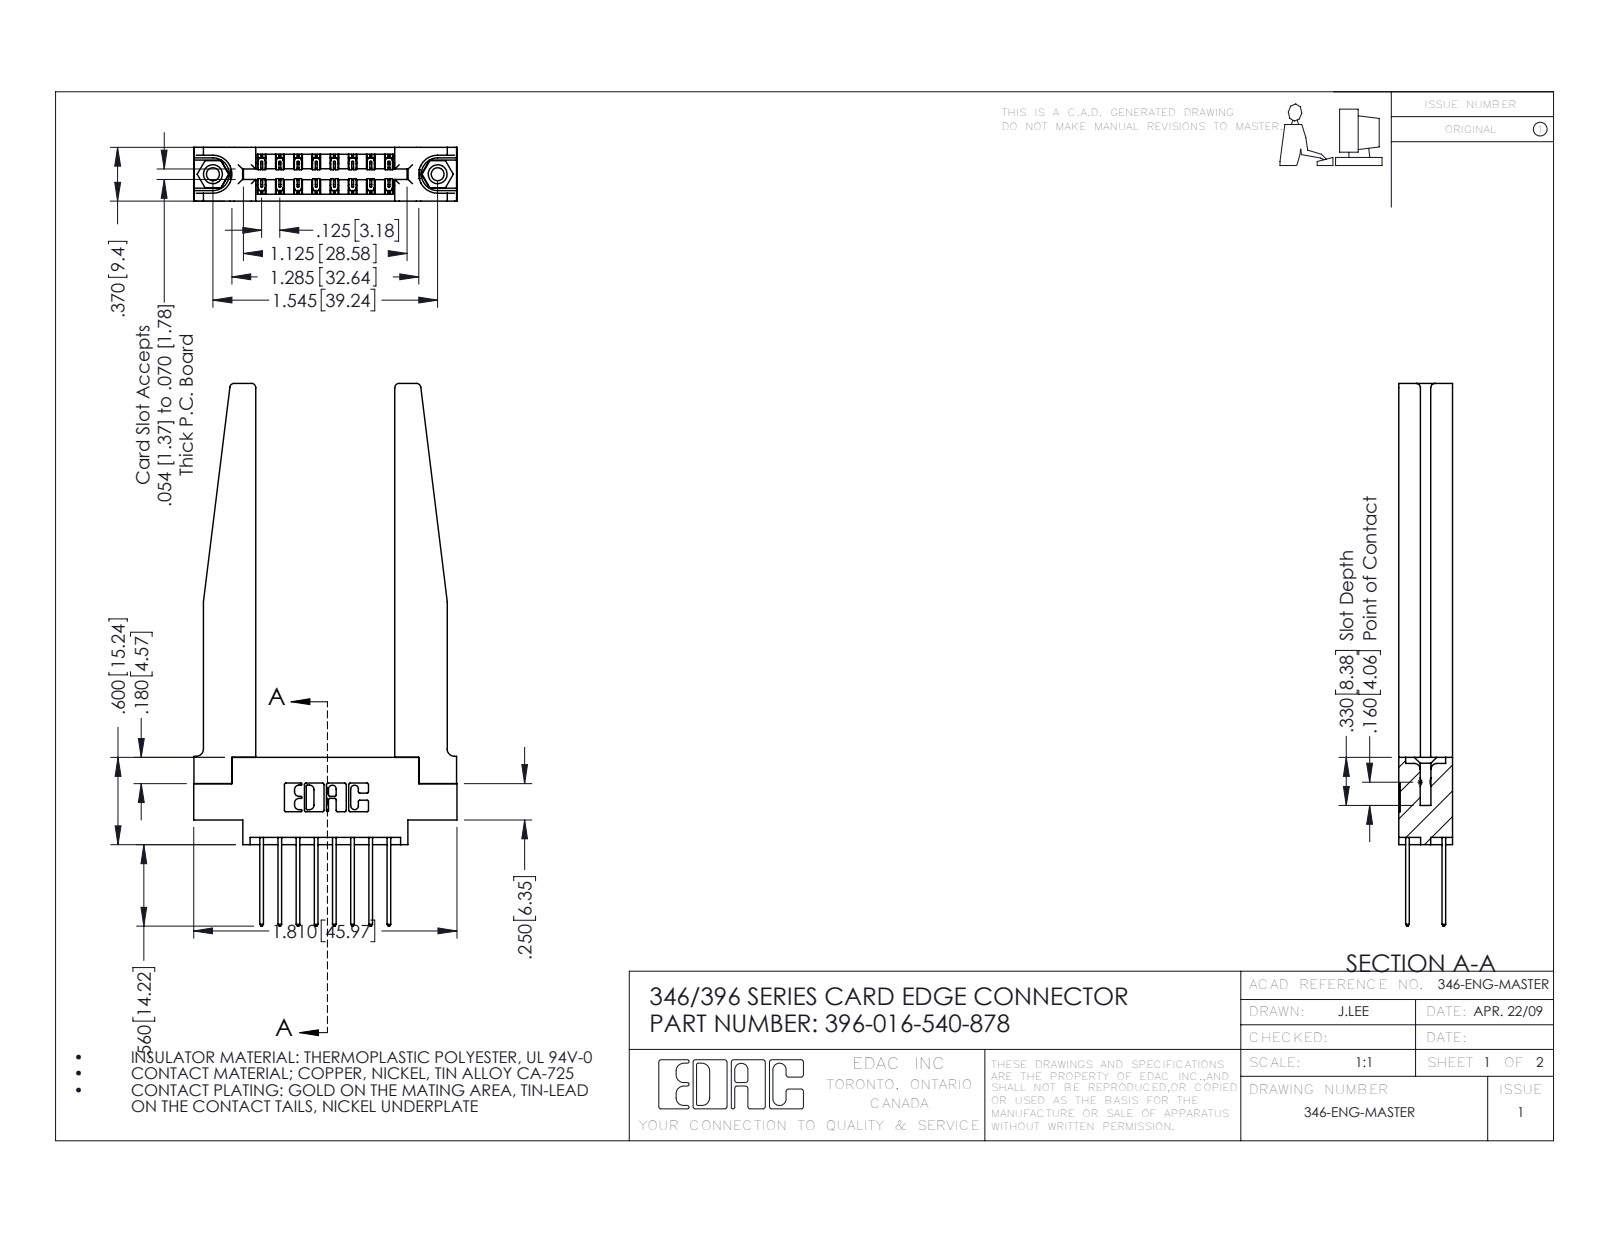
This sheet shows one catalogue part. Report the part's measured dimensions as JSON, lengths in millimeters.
{"part_name": "346-220-078_345-220-078; 346 Part_0.170 Offset - 0.156 Dia-TH; 345-292-001_345-293-140; 396-016-540-878 (+1 more)", "step_written_by": "SolidWorks 2016 (CONFIG_CONTROL_DESIGN)", "units": "millimeters", "bodies": {"solids": 21, "faces": 1192, "planar": 782, "cylindrical": 358, "other": 52}, "overall_size": [94.7, 46, 9.4], "volume_mm3": 11000, "surface_area_mm2": 12140, "round_holes": [[2.3, 2], [3.2, 2], [4, 2], [1.6, 1]], "round_bosses_or_shafts": [[3.9, 2]], "partial_cylinders_radius": [[0.2, 24], [0.3, 22], [0.3, 16], [0.8, 8], [0.2, 6], [0.8, 6], [0.7, 3], [0.4, 2]], "face_to_face_distances": [9.4, 3.8, 1.8, 3.8, 6.4, 1.2, 8.2, 2.6, 5.6, 4.4], "hole_center_spacings": [6.2, 34.1, 39.2]}
